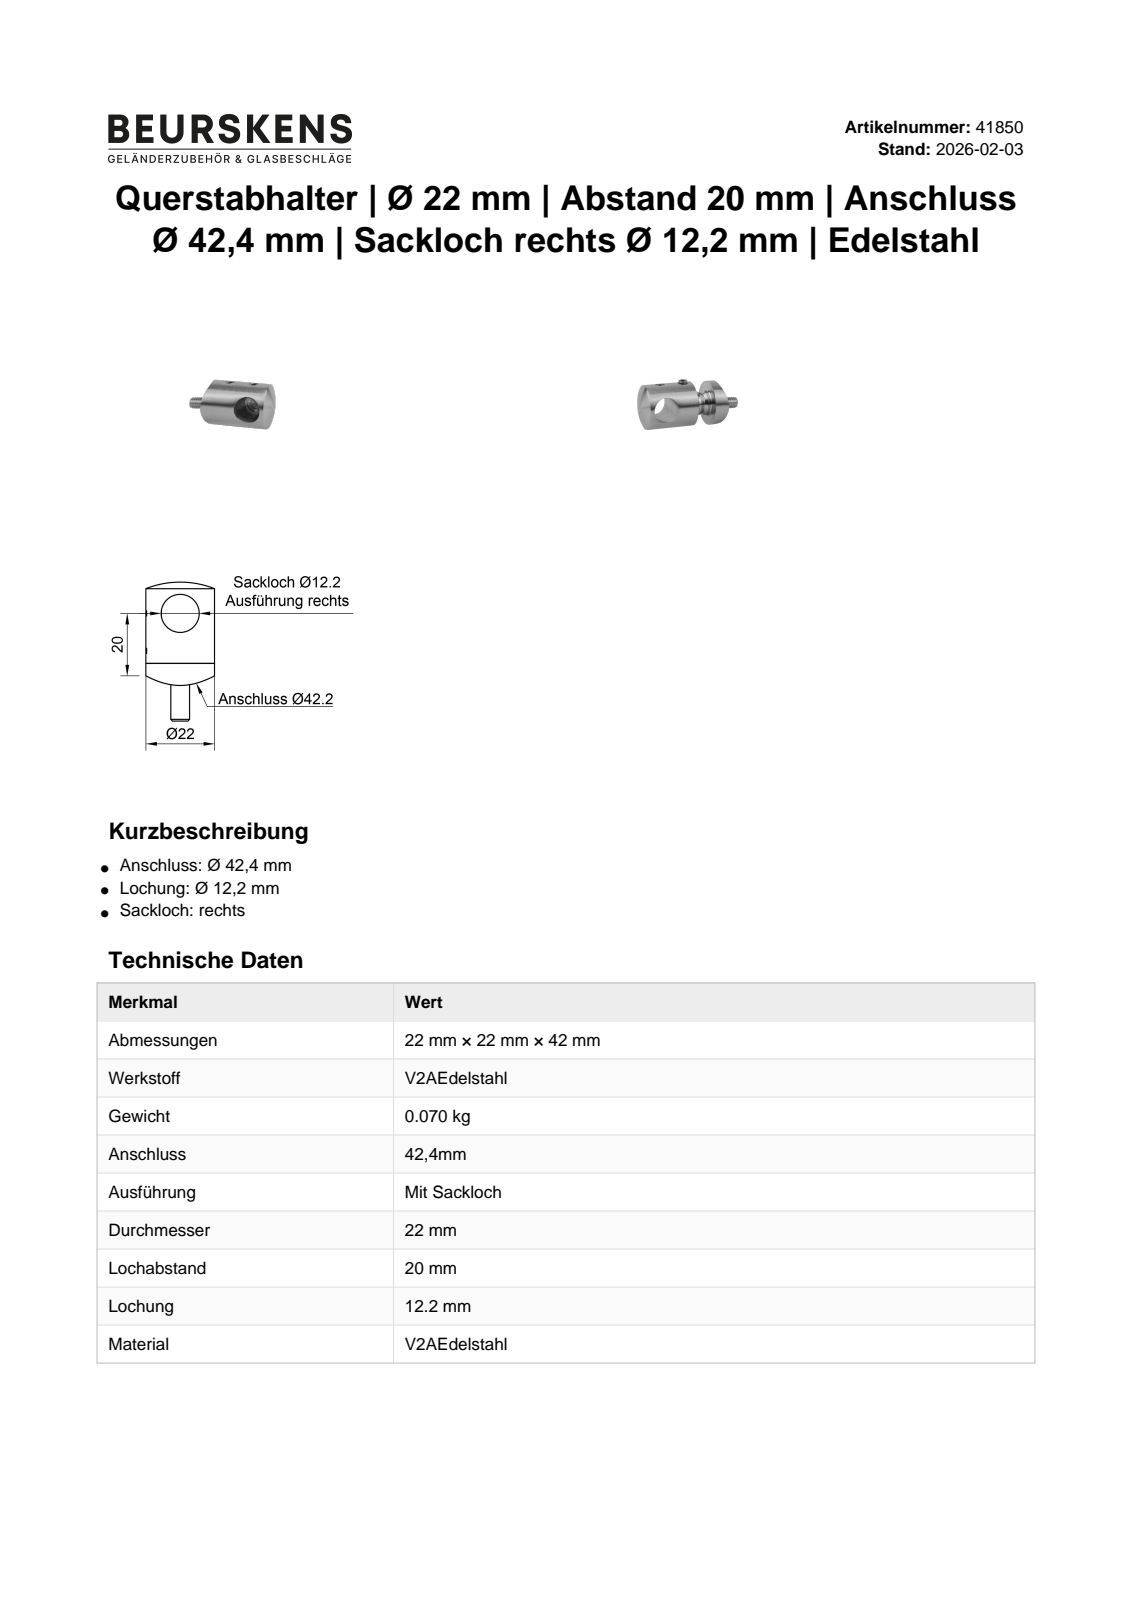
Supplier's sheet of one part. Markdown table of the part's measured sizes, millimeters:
| quantity | value |
| --- | --- |
| part name | 41850 for customer; socket countersunk head screw_din_DIN 7991 - M6 x 25 --- 18.7N; H-22-42.4ñ; socket set screw flat point_din_DIN 913 - M5 x 5-N |
| STEP written by | SolidWorks 2020 (CONFIG_CONTROL_DESIGN) |
| units | millimeters |
| bodies | 5 solids, 97 faces (38 planar, 27 cylindrical, 32 other) |
| overall size | 44.48 × 22 × 22 |
| volume | 9 392 mm³ |
| surface area | 5 887 mm² |
| round holes (diameter × count) | 4 × 2, 7 × 1, 11.2 × 1, 12.2 × 1, 14 × 1 |
| round bosses / shafts (diameter × count) | 5 × 2, 22 × 1, 12.8 × 1, 11.57 × 1, 6 × 1 |
| partial cylindrical surfaces (radius × count) | 21.2 × 1 |
| main face-to-face distances | 2, 6.51, 9.5, 8.51, 11.5, 2.99, 6, 3.5, 16.49, 18.49 |
| hole center spacings | 12 |
